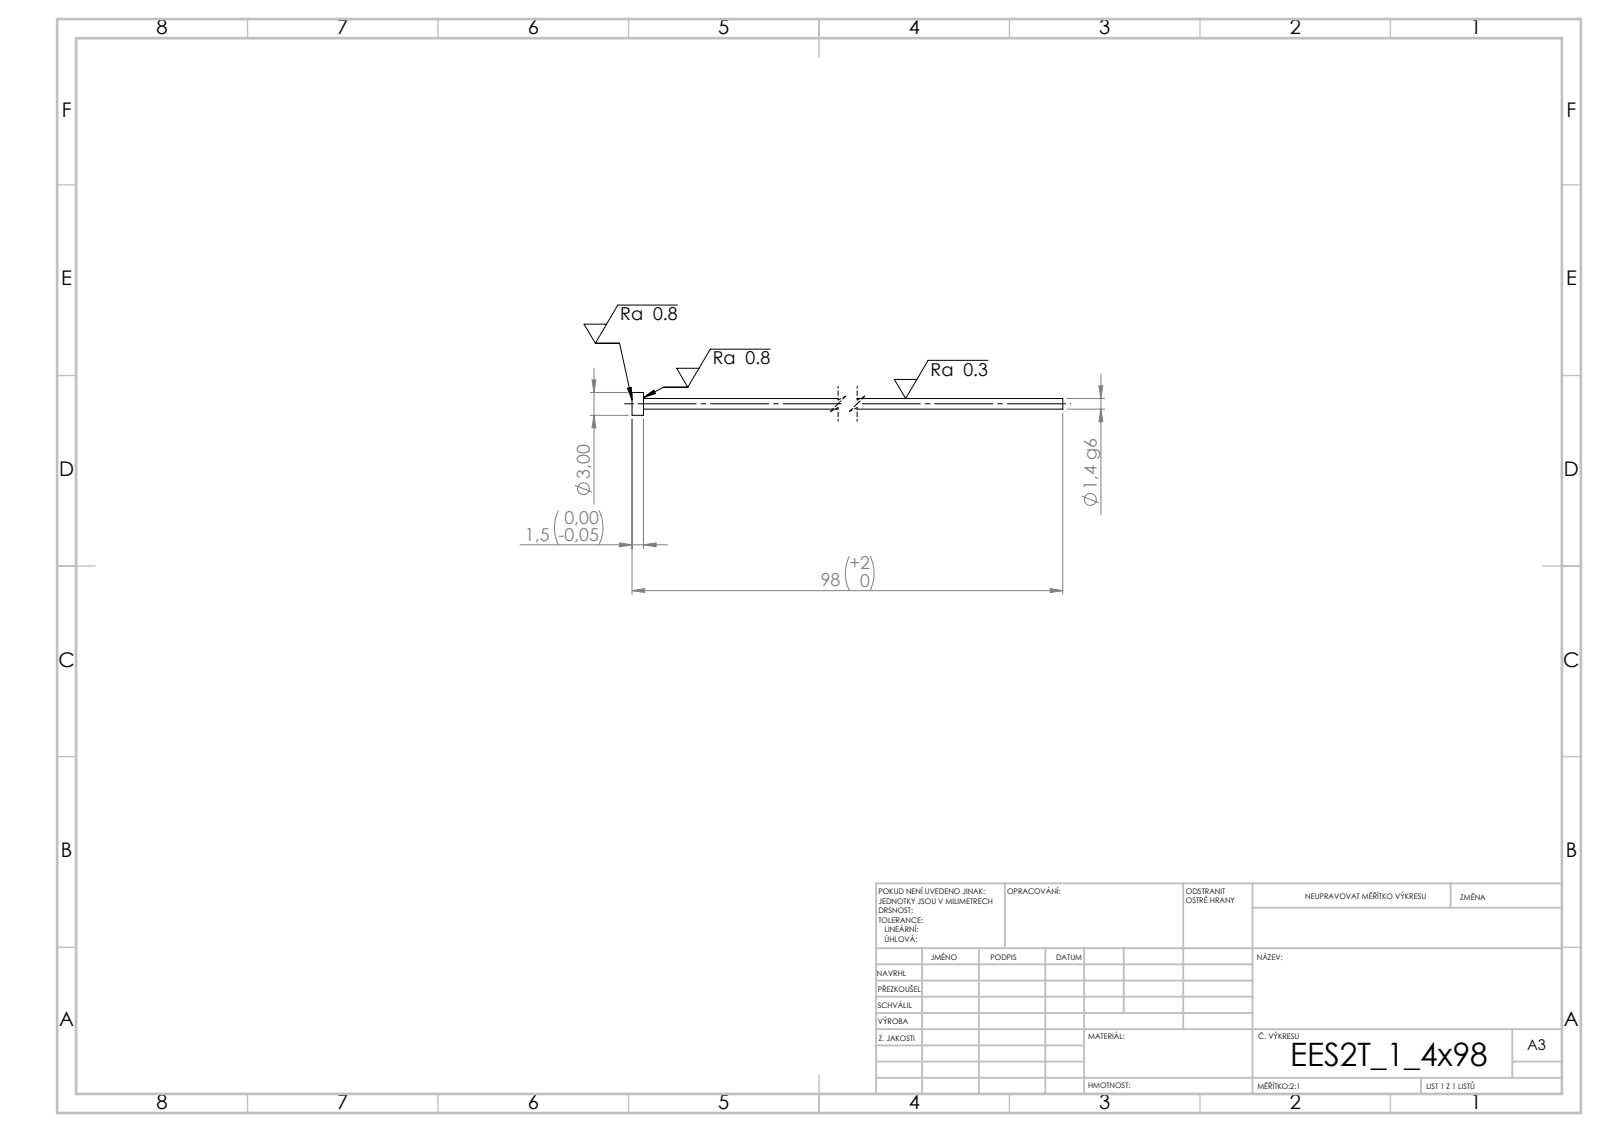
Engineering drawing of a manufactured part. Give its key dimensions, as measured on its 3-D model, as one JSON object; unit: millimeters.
{"step_written_by": "SolidWorks 2019 (CONFIG_CONTROL_DESIGN)", "units": "millimeters", "bodies": {"solids": 1, "faces": 7, "planar": 3, "cylindrical": 4, "other": 0}, "overall_size": [98, 3, 3], "volume_mm3": 159, "surface_area_mm2": 453, "round_bosses_or_shafts": [[3, 1], [1.4, 1]], "face_to_face_distances": [1.5, 98, 96.5]}
